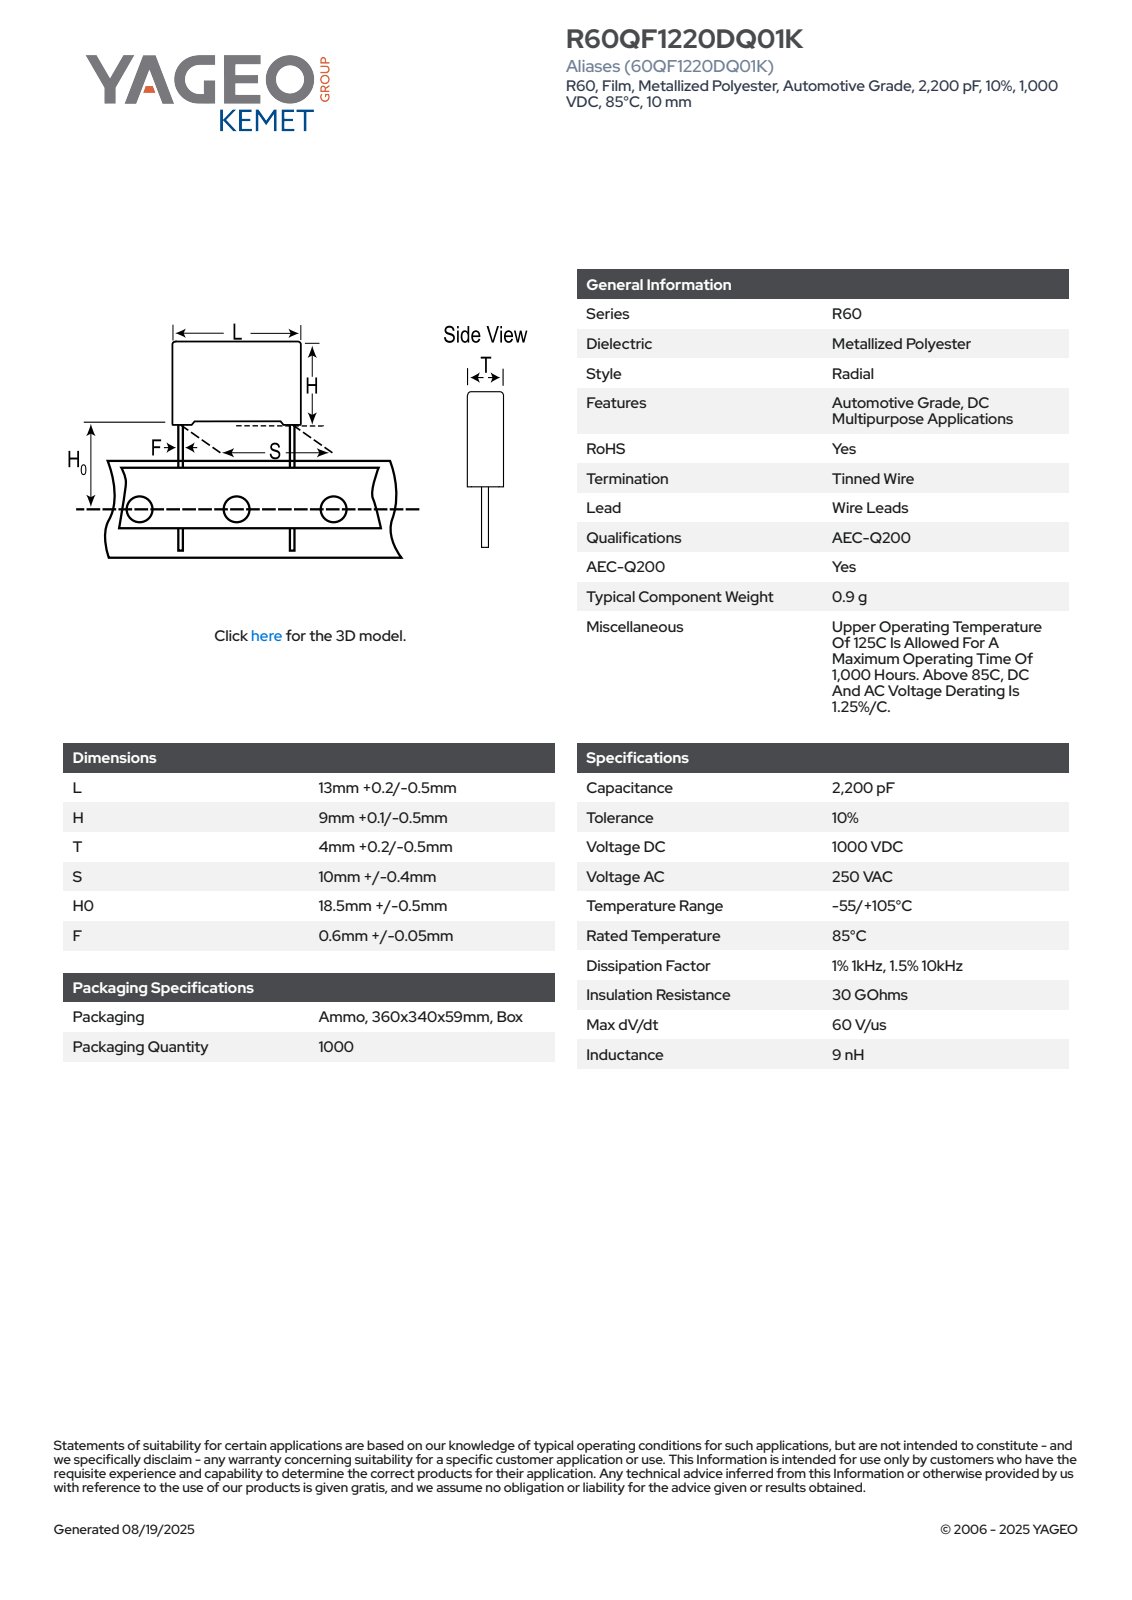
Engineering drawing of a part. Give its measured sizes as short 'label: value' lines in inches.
name: CFR_RB2_13X9X4_L13.2H9.1T4.2S10H019F0.65
written by: SolidWorks 2020 (AUTOMOTIVE_DESIGN)
unit: in
bodies: 4 solids, 85 faces (77 planar, 8 cylindrical, 0 other)
size: 1.106 × 0.52 × 0.166
volume: 0.029 in³; area: 0.82 in²
bosses: 2× ⌀0.026
rounds: 4× R0.02
face distances: 0.165, 0.329, 0.52, 0.017, 0.148, 0.03, 0.358, 0.131, 0.012, 0.346
